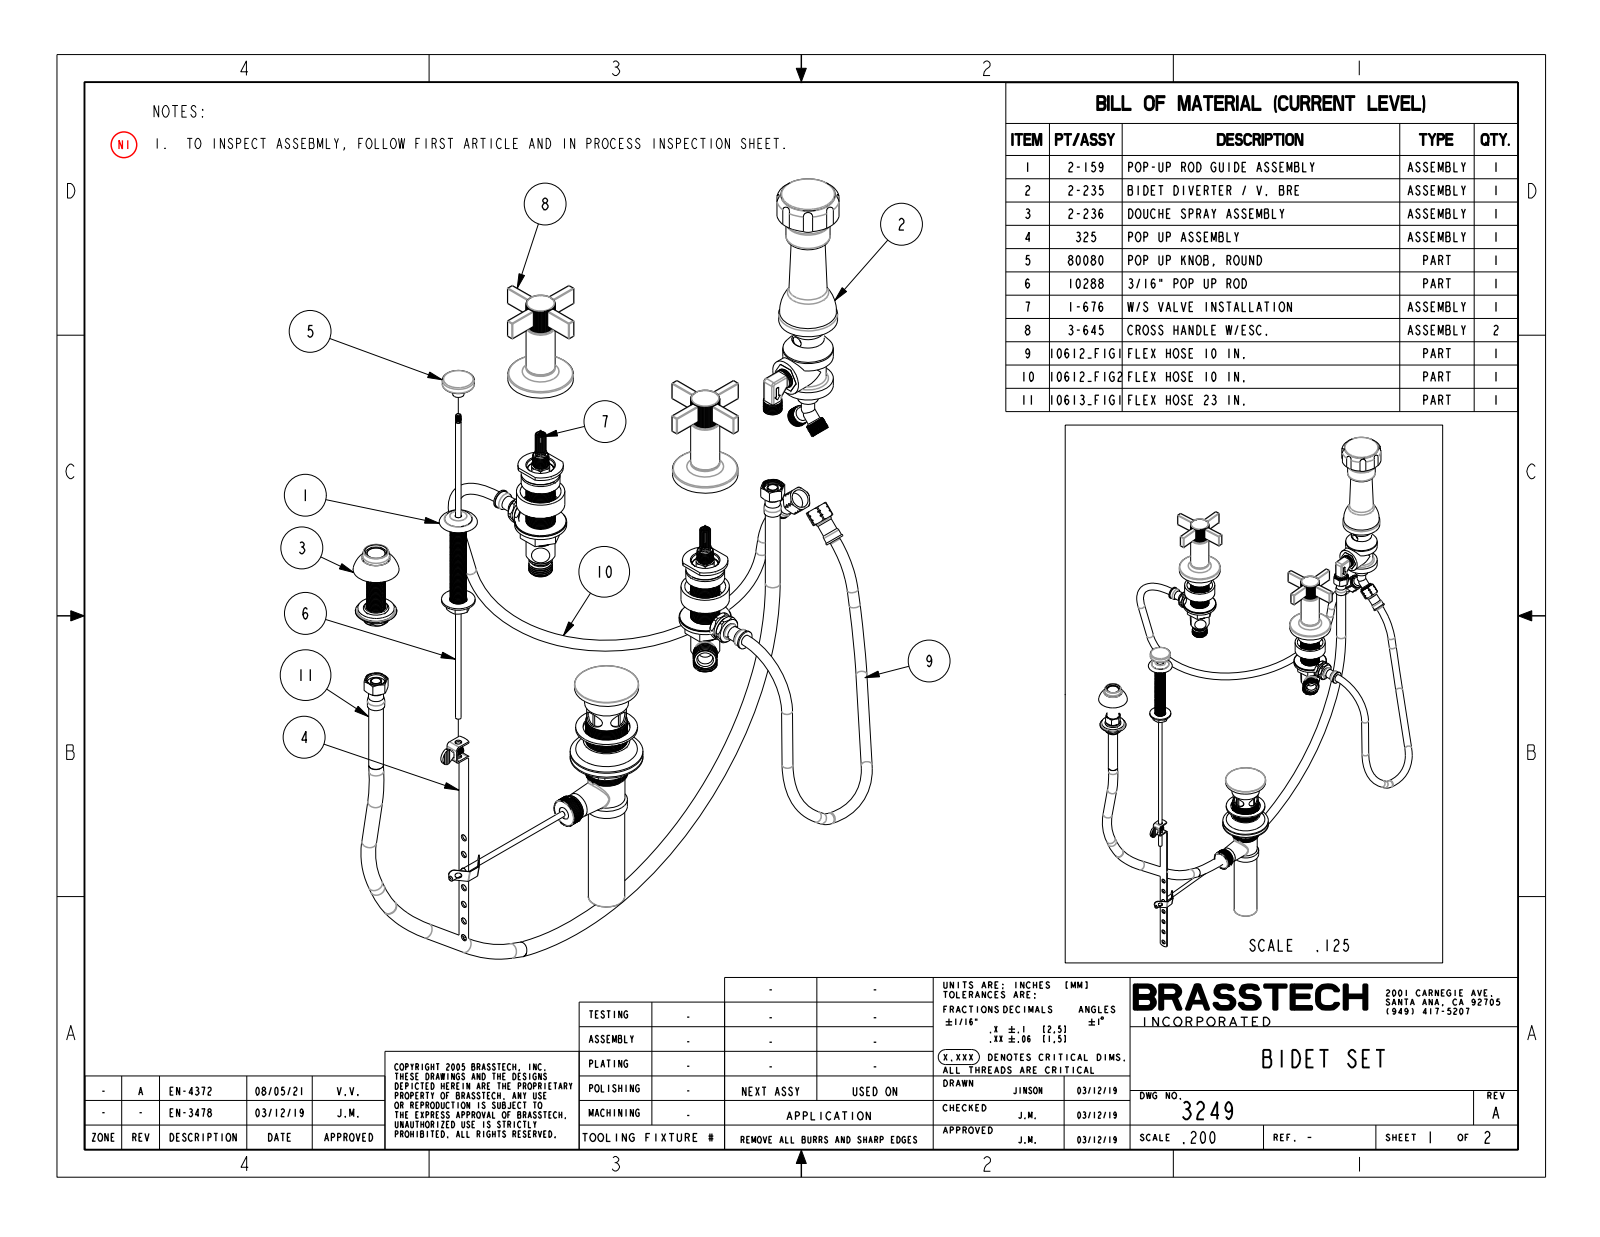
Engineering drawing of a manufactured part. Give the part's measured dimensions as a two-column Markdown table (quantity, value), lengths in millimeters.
| quantity | value |
| --- | --- |
| part name | 10078; 2-159_ASM; 91093; 10600 (+8 more) |
| STEP written by | CREO PARAMETRIC BY PTC INC, 2018400 (CONFIG_CONTROL_DESIGN) |
| units | millimeters |
| bodies | 49 solids, 5285 faces (1772 planar, 2207 cylindrical, 1306 other) |
| overall size | 580.5 × 279.4 × 136.5 |
| volume | 187 500 mm³ |
| surface area | 198 800 mm² |
| round holes (diameter × count) | 2.8 × 10, 3.8 × 9, 15.2 × 3, 3.6 × 2, 7 × 2, 8.5 × 2, 9.1 × 2, 9.5 × 2, 9.7 × 2, 10.1 × 2, 10.2 × 2, 10.7 × 2 |
| round bosses / shafts (diameter × count) | 3.5 × 10, 57.2 × 2, 46 × 2, 25.4 × 2, 21.6 × 2, 18.5 × 2, 14.5 × 2, 13.2 × 2 |
| partial cylindrical surfaces (radius × count) | 0.5 × 68, 1.3 × 30, 2.8 × 30, 4.7 × 30, 2.5 × 18, 0.3 × 12, 0.8 × 12, 1.1 × 12 |
| main face-to-face distances | 6.4, 203.2, 6.4, 59, 17.9, 1.4, 63.4, 79.9, 16.5, 4.4 |
| hole center spacings | 8.5, 12, 203.2, 17, 194.9, 203.4, 211.9, 194.7 |
